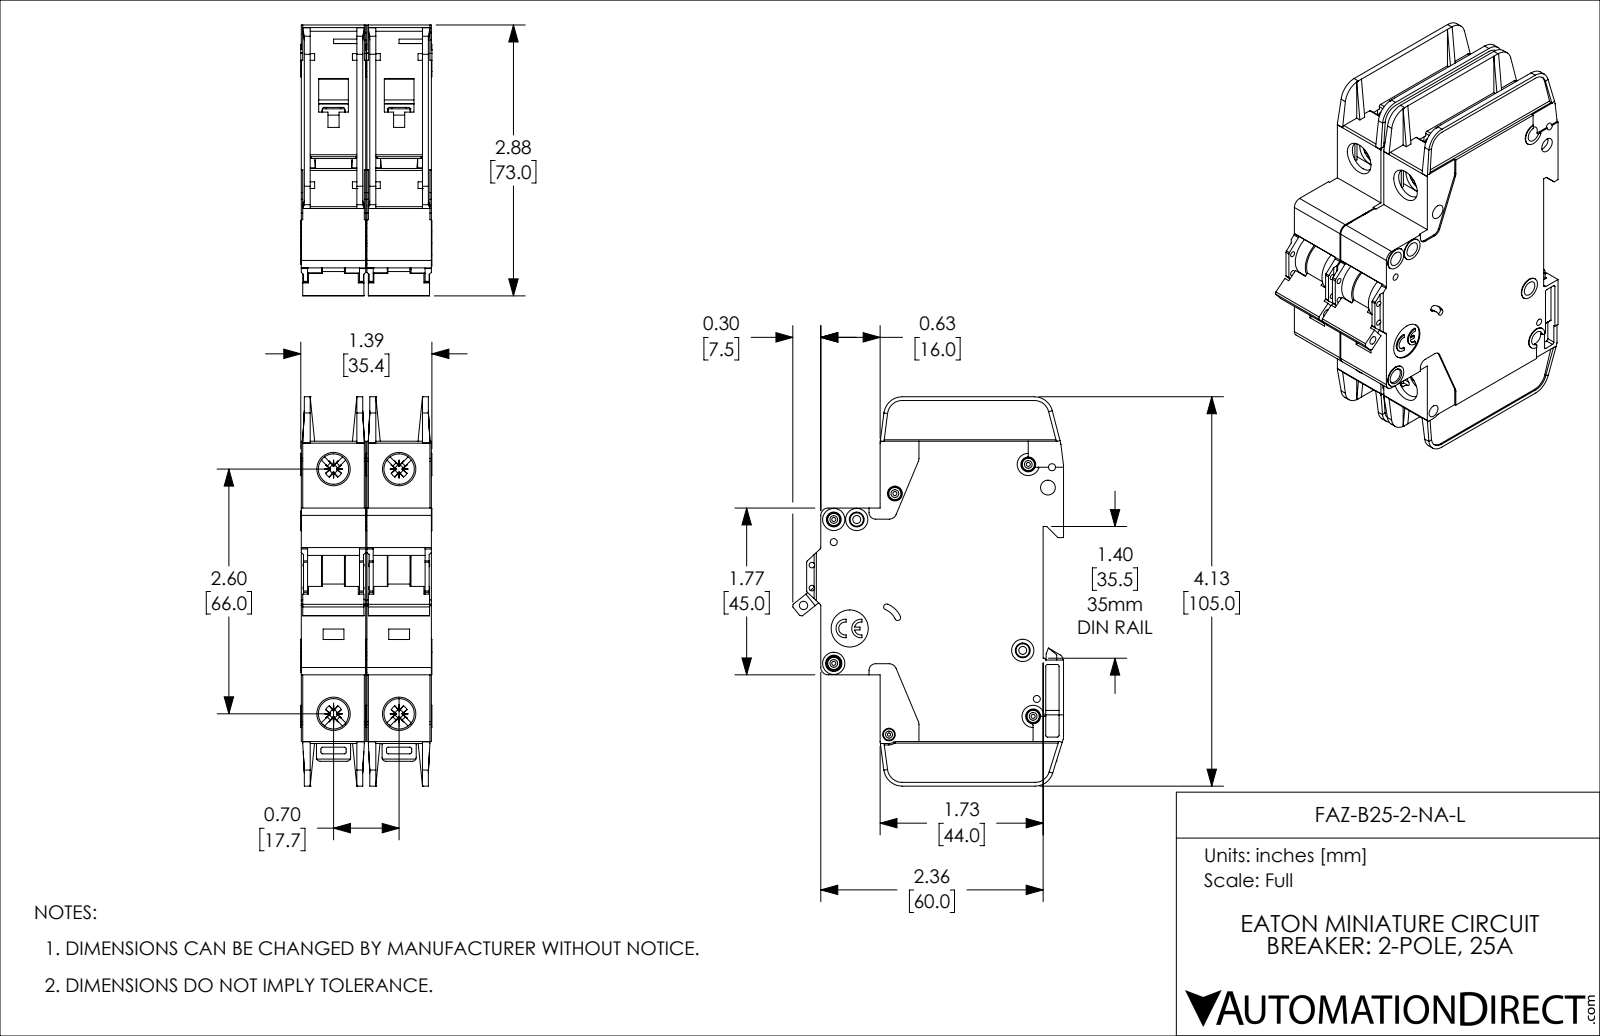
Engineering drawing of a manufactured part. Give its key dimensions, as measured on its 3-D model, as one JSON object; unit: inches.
{"part_name": "FAZ-B25-2-NA-L", "step_written_by": "SolidWorks 2019 (AUTOMOTIVE_DESIGN)", "units": "inches", "bodies": {"solids": 2, "faces": 2254, "planar": 1342, "cylindrical": 714, "other": 198}, "overall_size": [4.134, 2.876, 1.394], "volume_in3": 9.365, "surface_area_in2": 82.01, "round_holes": [[0.157, 8], [0.043, 5], [0.075, 4], [0.323, 4], [0.059, 2], [0.085, 2], [0.035, 1], [0.089, 1], [0.098, 1], [0.134, 1], [0.394, 1]], "round_bosses_or_shafts": [[0.13, 5], [0.236, 4], [0.118, 3], [0.098, 2]], "partial_cylinders_radius": [[0.02, 57], [0.016, 20], [0.039, 14], [0.079, 10], [0.043, 8], [0.008, 5], [0.197, 5], [0.01, 4]], "face_to_face_distances": [0.697, 0.047, 0.685, 0.591, 0.094, 0.638, 0.543, 1.382, 0.744, 0.65], "hole_center_spacings": [0.244, 0.537, 0.697, 0.87, 2.598, 2.69, 0.189, 0.199]}
